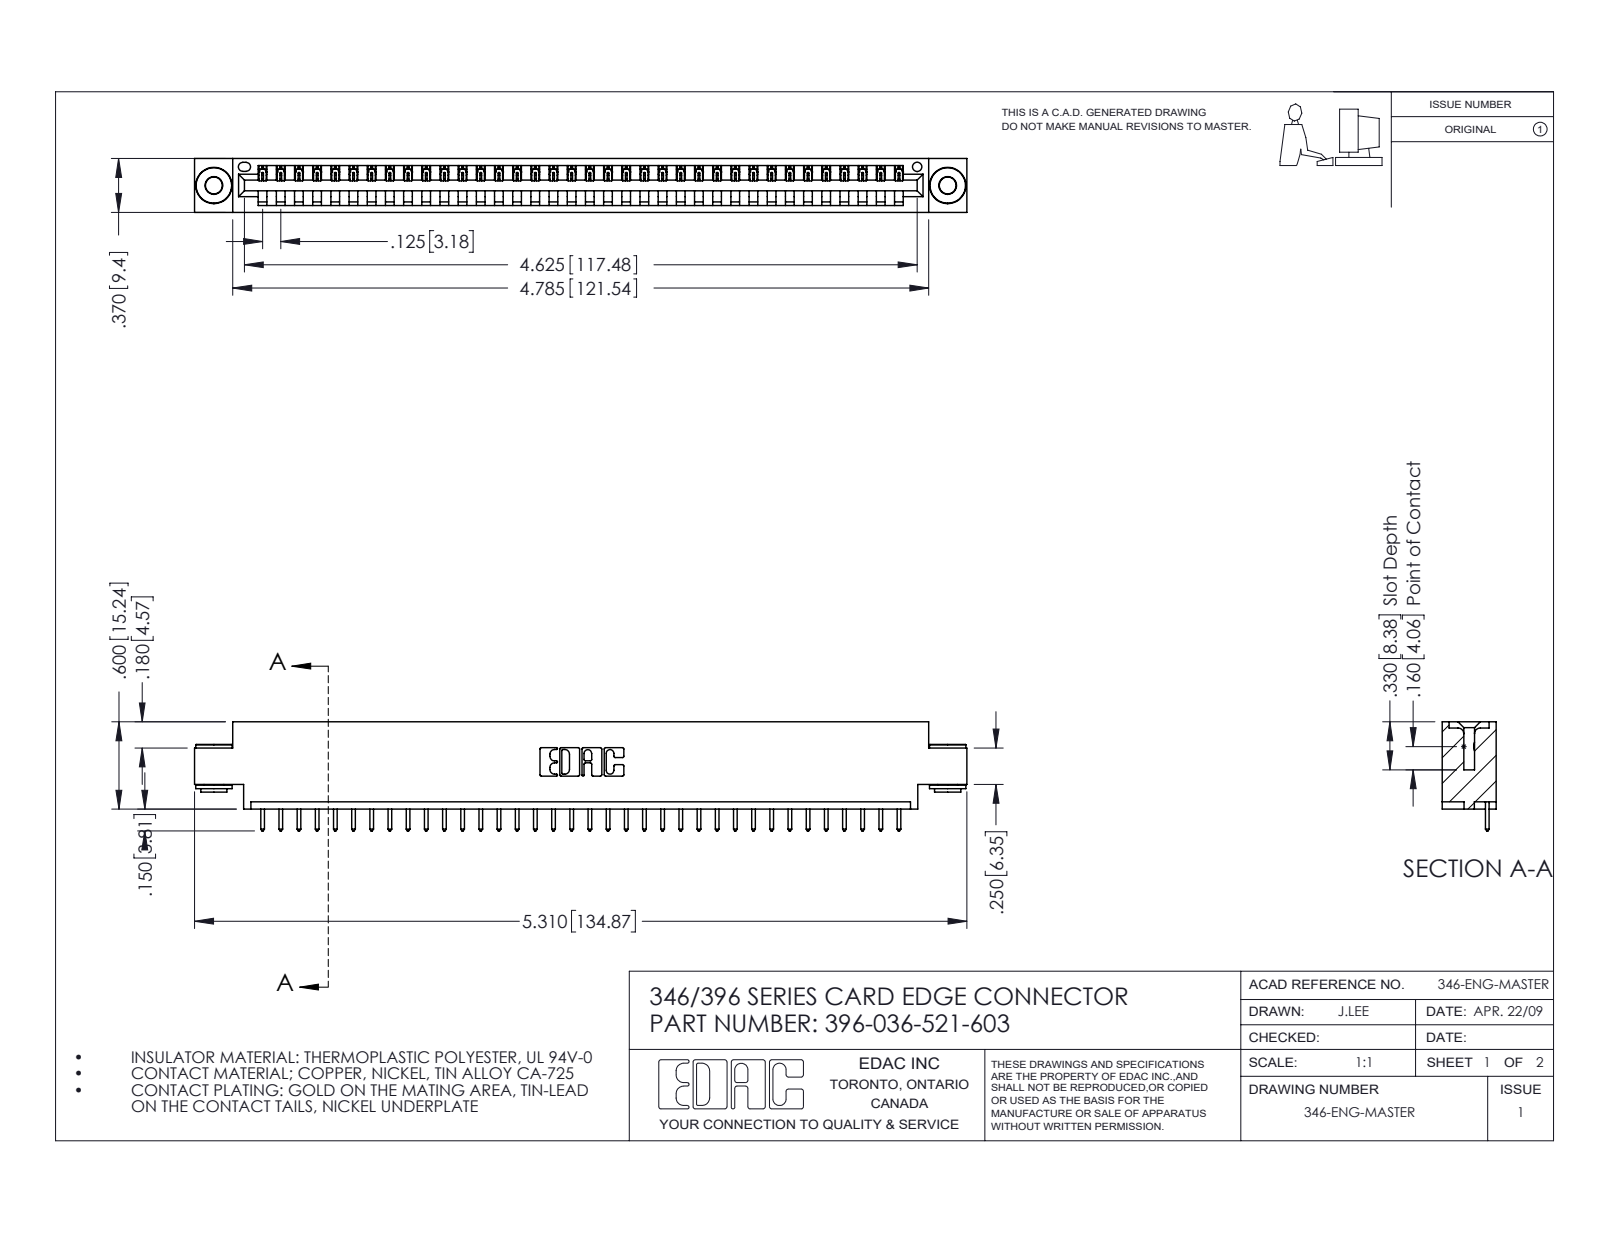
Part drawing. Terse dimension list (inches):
name: 346 Part_0.170 Offset - 0.156 Dia-TH; 396-036-521-603; 345-250-002_345-250-002-102; 345-292-001_345-293-121
written by: SolidWorks 2016 (CONFIG_CONTROL_DESIGN)
unit: in
bodies: 39 solids, 2252 faces (1530 planar, 714 cylindrical, 8 other)
size: 5.31 × 0.75 × 0.37
volume: 0.771 in³; area: 24.33 in²
holes: 2× ⌀0.116, 2× ⌀0.156, 1× ⌀0.064
bosses: 2× ⌀0.25, 2× ⌀0.18, 2× ⌀0.136
rounds: 72× R0.006, 72× R0.01, 22× R0.01, 6× R0.007, 6× R0.031, 3× R0.026, 2× R0.031, 2× R0.04
face distances: 0.048, 0.322, 0.37, 0.25, 0.025, 0.072, 0.298, 0.148, 0.222, 0.1
hole spacings: 0.246, 4.836, 5.045
